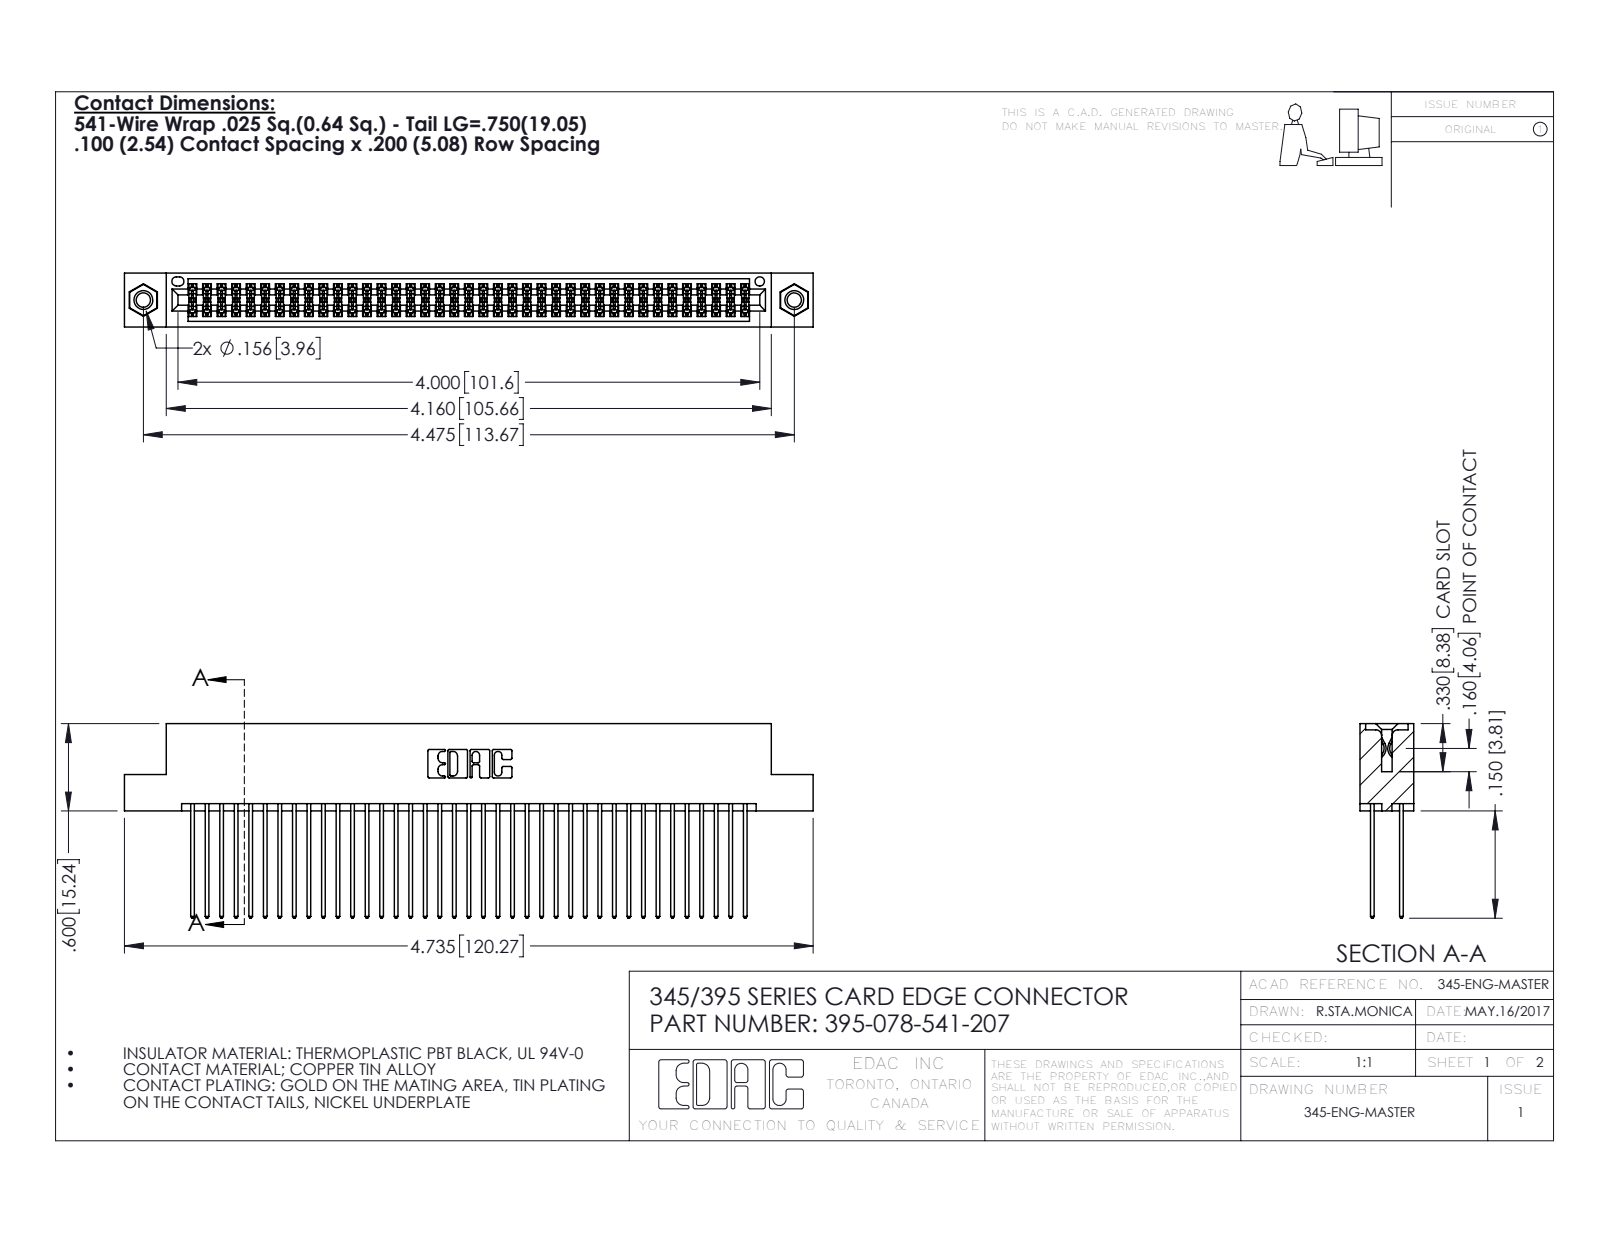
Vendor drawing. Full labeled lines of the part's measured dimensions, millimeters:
Part name (STEP PRODUCT): 345-292-001_345-293-141; 395-078-541-207; 345-250-001_345-250-005-103; 345 Part_Flush Mounting Lugs - 0.156 Dia-TI
STEP written by: SolidWorks 2016 (CONFIG_CONTROL_DESIGN)
Units: millimetres
Bodies: 81 solids, 4086 faces (2686 planar, 1384 cylindrical, 16 other)
Overall size (bounding box): 120.3 × 34 × 9.4
Volume: 12 100 mm³ · Surface area: 19 940 mm²
Round holes (diameter × count): ⌀2.5 ×2, ⌀3.2 ×2, ⌀4 ×2, ⌀1.6 ×1
Round bosses / shafts (diameter × count): ⌀3.9 ×2
Partial cylindrical surfaces — rounded edges, fillets, slot ends (radius × count): R0.2 ×117, R0.3 ×78, R0.3 ×22, R0.2 ×6, R0.8 ×6, R0.7 ×3, R0.4 ×2, R0.5 ×2
Main face-to-face distances: 1.8, 7.6, 5.1, 2.5, 6.9, 0.6, 5.7, 9.4, 4.4, 3.8
Hole centre spacings: 6.9, 107.7, 113.7
